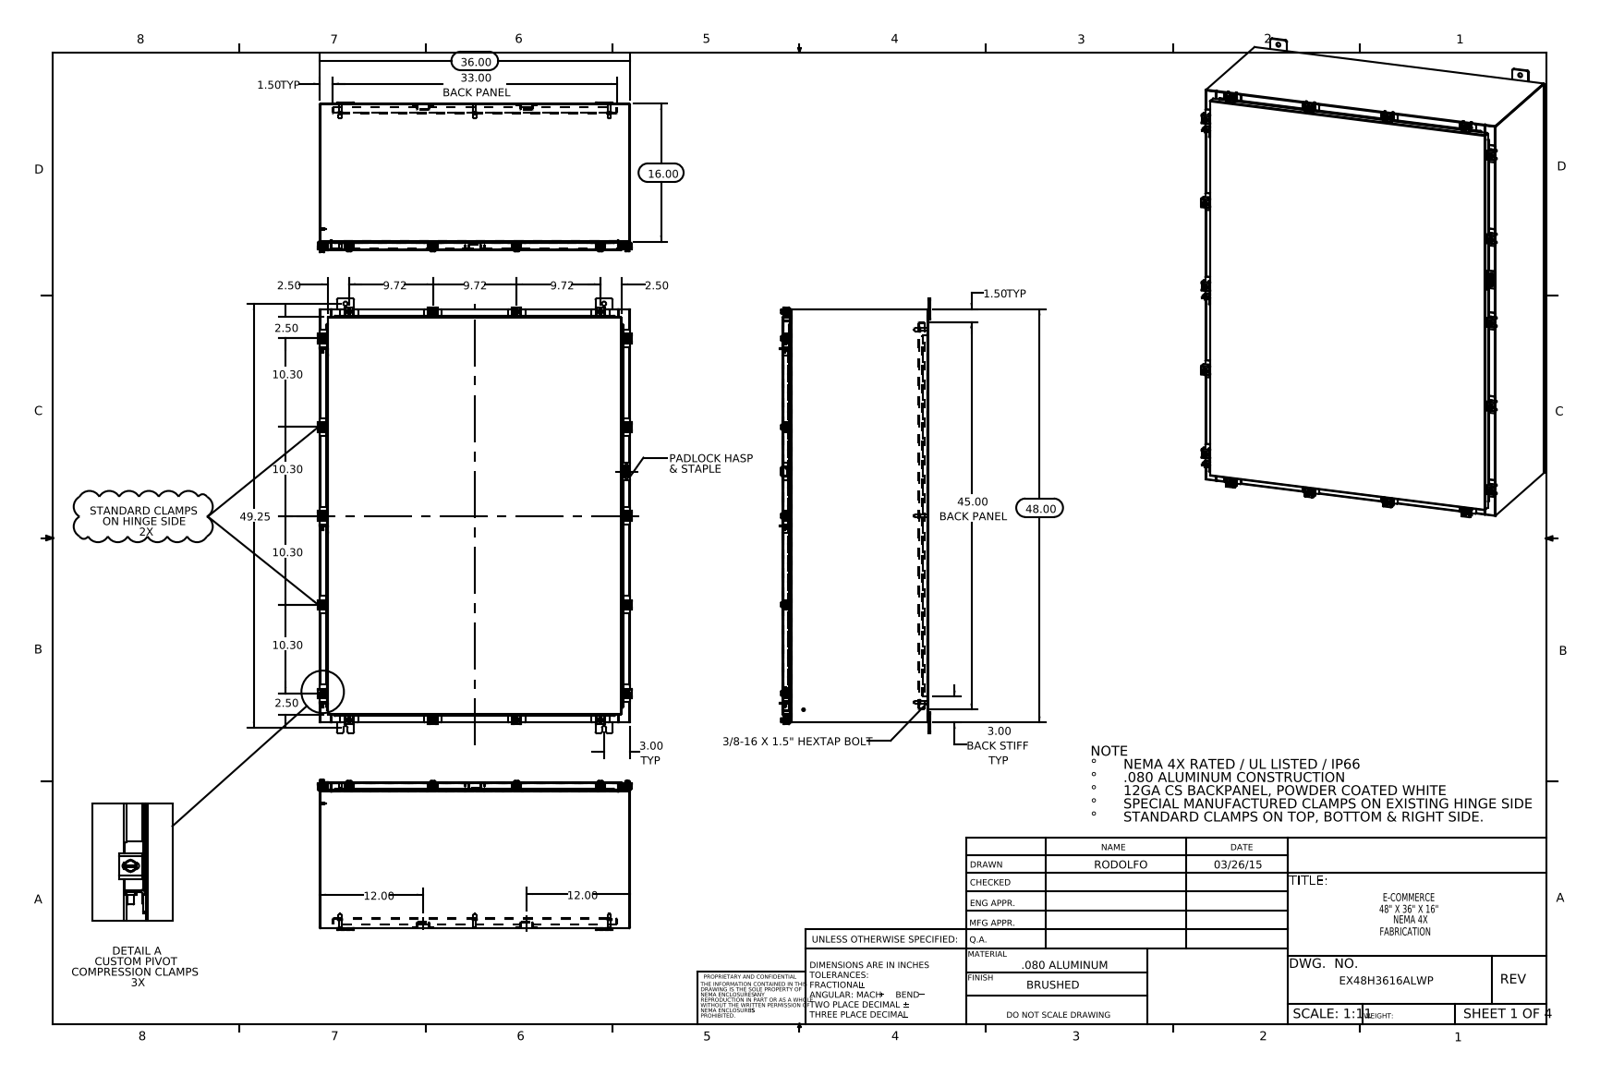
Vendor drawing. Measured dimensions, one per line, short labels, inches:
name: EX48H3616ALWP Enclosure Stiffener; Special Clamp Assembly; 30X10 Clamp Bracket2; 10_30 CD Stud (+8 more)
written by: SolidWorks 2014 (CONFIG_CONTROL_DESIGN)
unit: in
bodies: 126 solids, 3106 faces (1613 planar, 1195 cylindrical, 298 other)
size: 50.5 × 36.421 × 17.453
volume: 698.7 in³; area: 17 479 in²
holes: 18× ⌀0.213, 18× ⌀0.26, 12× ⌀0.5, 7× ⌀0.25, 1× ⌀0.125
bosses: 18× ⌀0.5, 18× ⌀0.25, 15× ⌀0.399, 8× ⌀0.625, 8× ⌀0.375, 8× ⌀0.33, 6× ⌀0.157, 6× ⌀0.14
rounds: 76× R0.06, 38× R0.013, 36× R0.141, 34× R0.088, 33× R0.12, 27× R0.09, 25× R0.05, 24× R0.145
face distances: 0.075, 16.9, 16.826, 16.975, 0.104, 35.925, 1, 1.075, 15.826, 15.9
hole spacings: 1.969, 2.347, 4.44, 13.972, 14.728, 16.126, 16.624, 17.756
